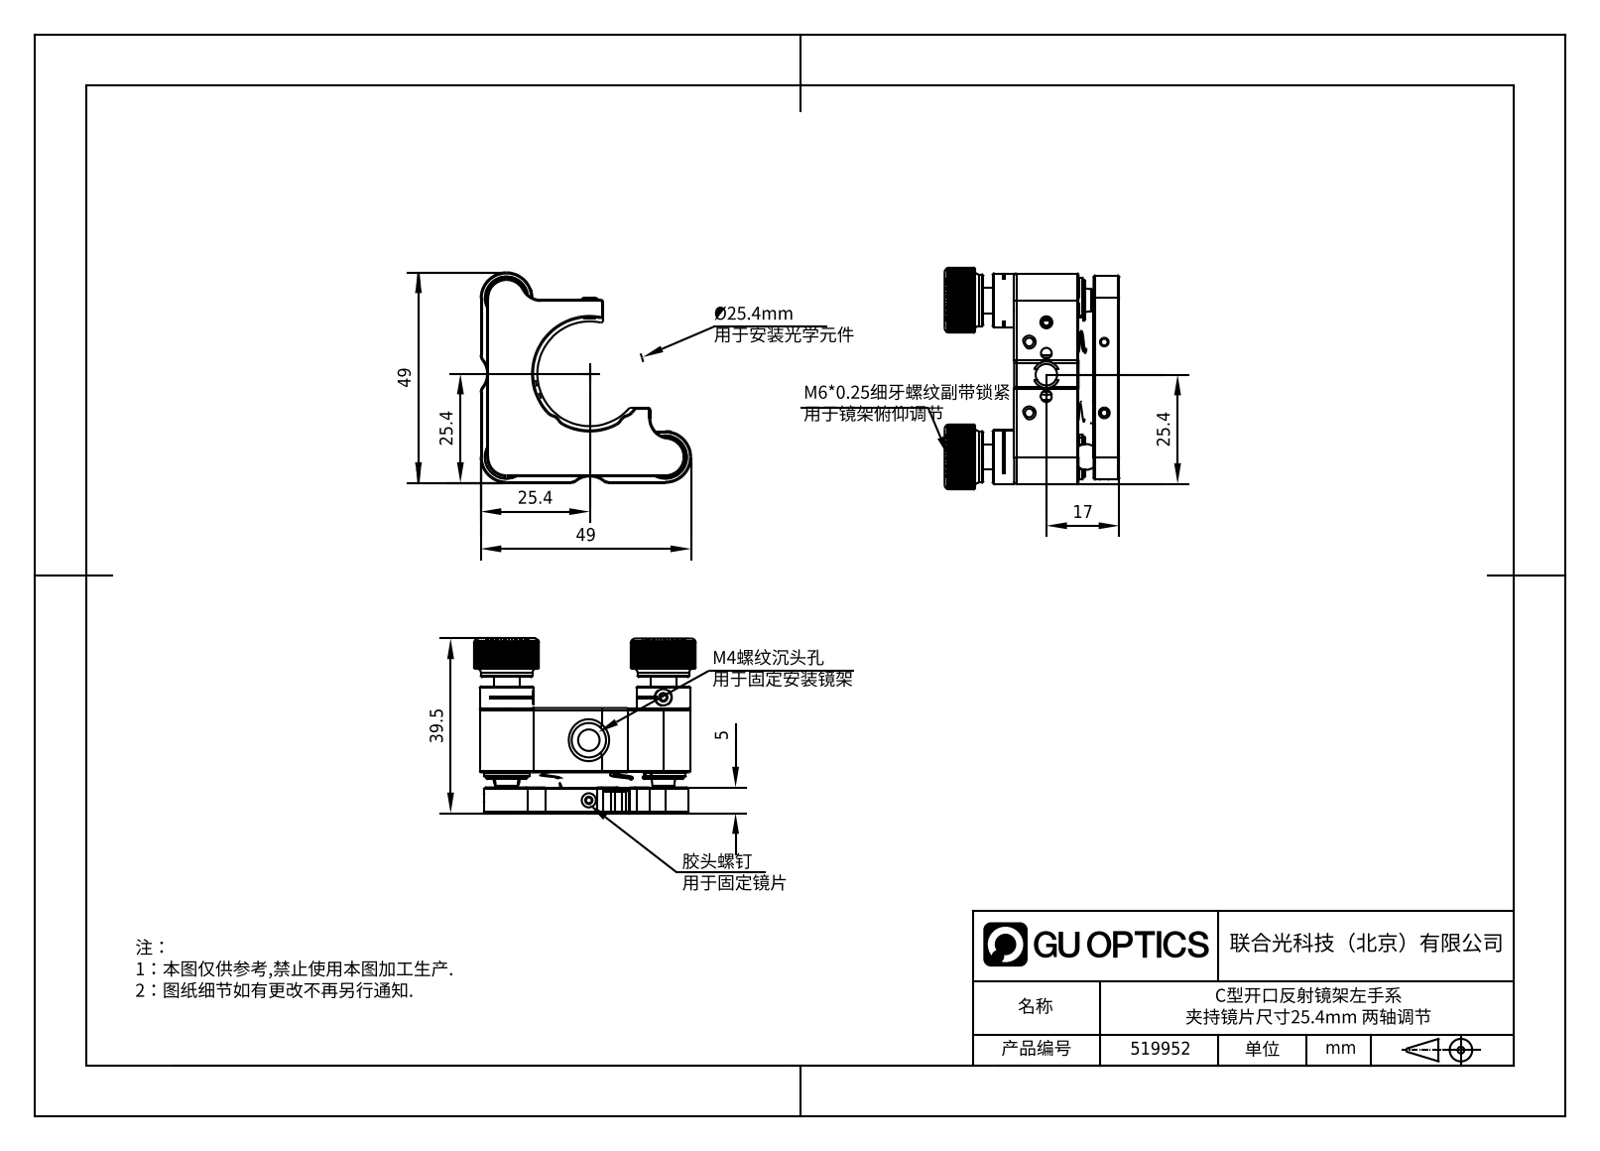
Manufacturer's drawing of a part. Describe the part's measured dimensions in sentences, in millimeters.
The part is named "519952". Its 3-D file was written by "SolidWorks 2020 (CONFIG_CONTROL_DESIGN)". It is 0 solids with 855 faces: 458 planar, 251 cylindrical and 146 other. Overall it measures 51.5 by 51.5 by 40.7 millimeters. Round holes: 4 of diameter 6, 3 of diameter 2.5, 2 of diameter 4.6, 2 of diameter 5, 2 of diameter 8, 2 of diameter 9.5, 2 of diameter 10.5, 2 of diameter 12, 1 of diameter 3.3. Round bosses or shafts: 5 of diameter 4, 4 of diameter 3, 2 of diameter 12.5, 2 of diameter 6, 2 of diameter 1.5, 1 of diameter 8, 1 of diameter 2.4. Partial cylindrical surfaces (rounded edges, fillets, slot ends): 7 of radius 2.5, 6 of radius 0.3, 6 of radius 0.8, 5 of radius 1.5, 4 of radius 0.5, 4 of radius 1, 4 of radius 1.25, 3 of radius 5.25. The main face-to-face distances are 6, 24.5, 1, 18.5, 3.5, 15, 9.5, 2.25, 2.75, 11.5. The hole center spacings are 5, 9.75, 16.5, 26.25, 28.65, 37.91, 45.25, 7.2.
